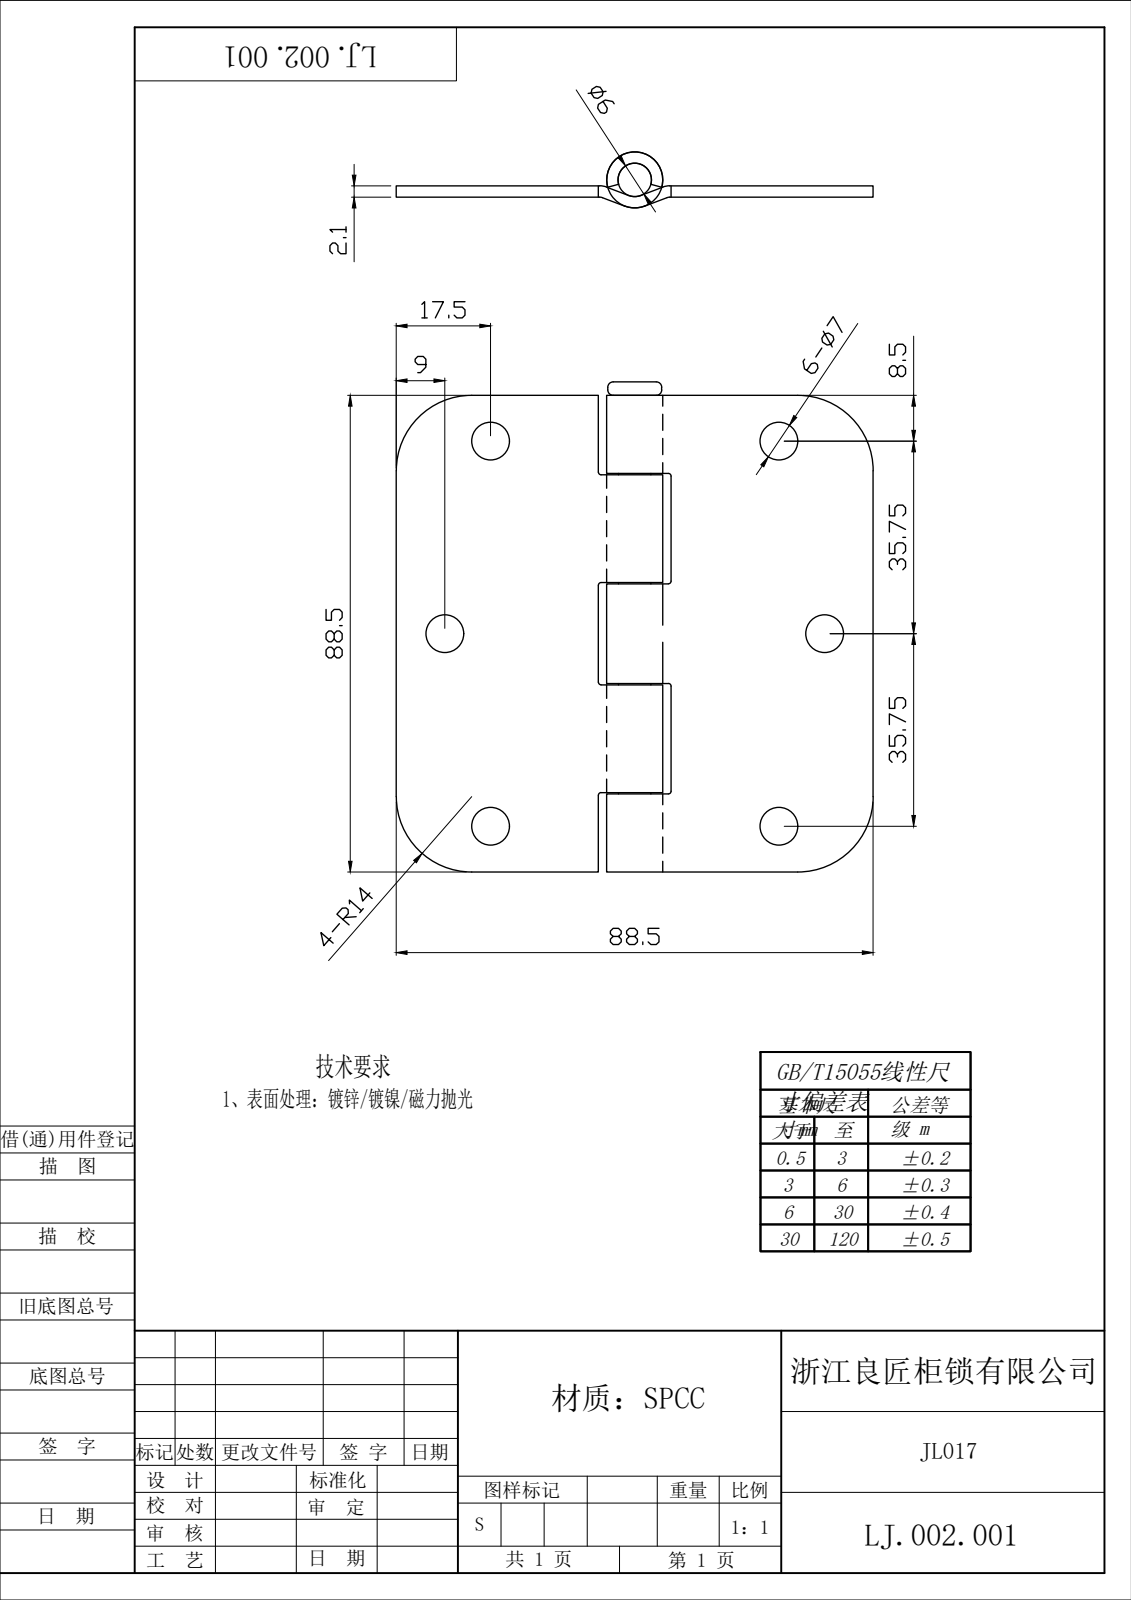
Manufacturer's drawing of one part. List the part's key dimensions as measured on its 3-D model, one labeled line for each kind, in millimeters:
STEP written by: Rhino 8.5 (CONFIG_CONTROL_DESIGN)
Units: millimetres
Bodies: 3 solids, 95 faces (49 planar, 42 cylindrical, 4 other)
Overall size (bounding box): 91 × 88.5 × 10.4
Volume: 20 848 mm³ · Surface area: 21 059 mm²
Round holes (diameter × count): ⌀7 ×6, ⌀6.2 ×1
Round bosses / shafts (diameter × count): ⌀10.4 ×1, ⌀10 ×1, ⌀6 ×1
Partial cylindrical surfaces — rounded edges, fillets, slot ends (radius × count): R14 ×4, R0.5 ×2, R1.5 ×2, R3.6 ×2
Main face-to-face distances: 2.1, 88.5, 37.5, 51, 39, 20.31, 14.75, 73.75, 34.75, 53.75
Hole centre spacings: 36.75, 71.57, 53.5, 71.5, 89.3, 70.5
